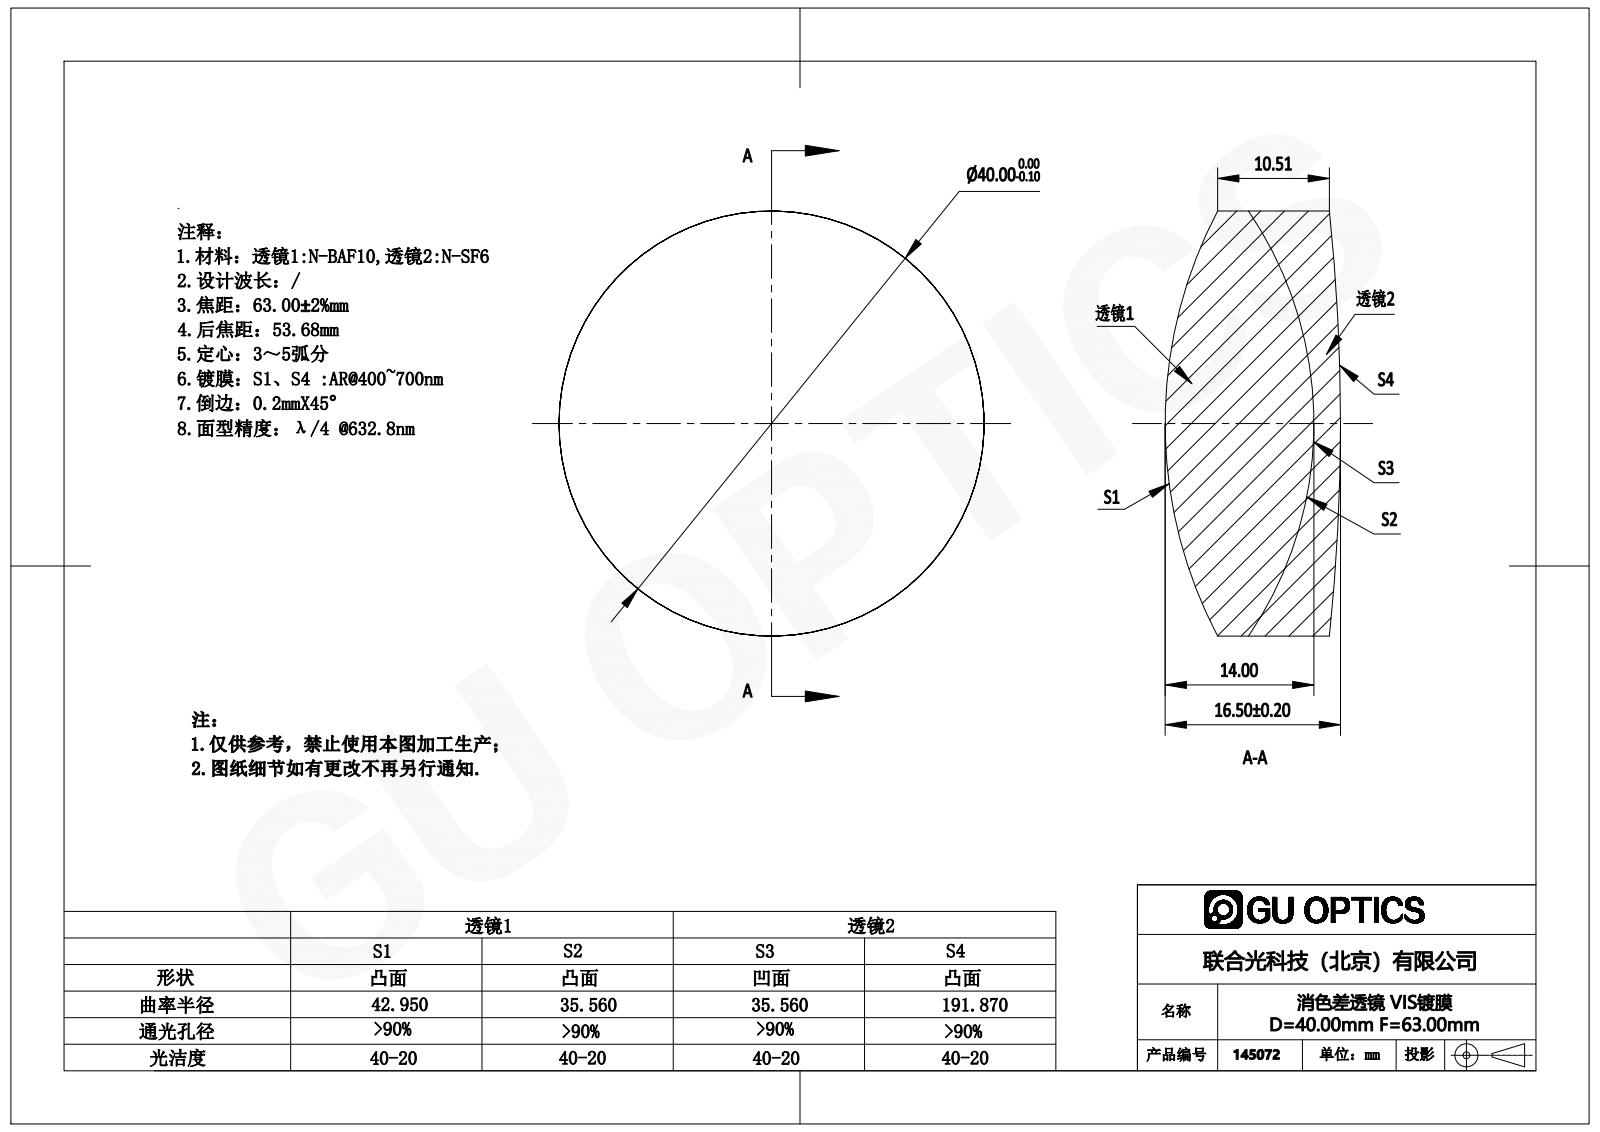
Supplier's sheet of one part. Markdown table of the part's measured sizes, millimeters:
| quantity | value |
| --- | --- |
| part name | 145072 |
| STEP written by | SolidWorks 2016 (AUTOMOTIVE_DESIGN) |
| units | millimeters |
| bodies | 2 solids, 12 faces (0 planar, 4 cylindrical, 8 other) |
| overall size | 40 × 40 × 16.5 |
| volume | 17 037 mm³ |
| surface area | 6 666 mm² |
| round bosses / shafts (diameter × count) | 40 × 1 |
